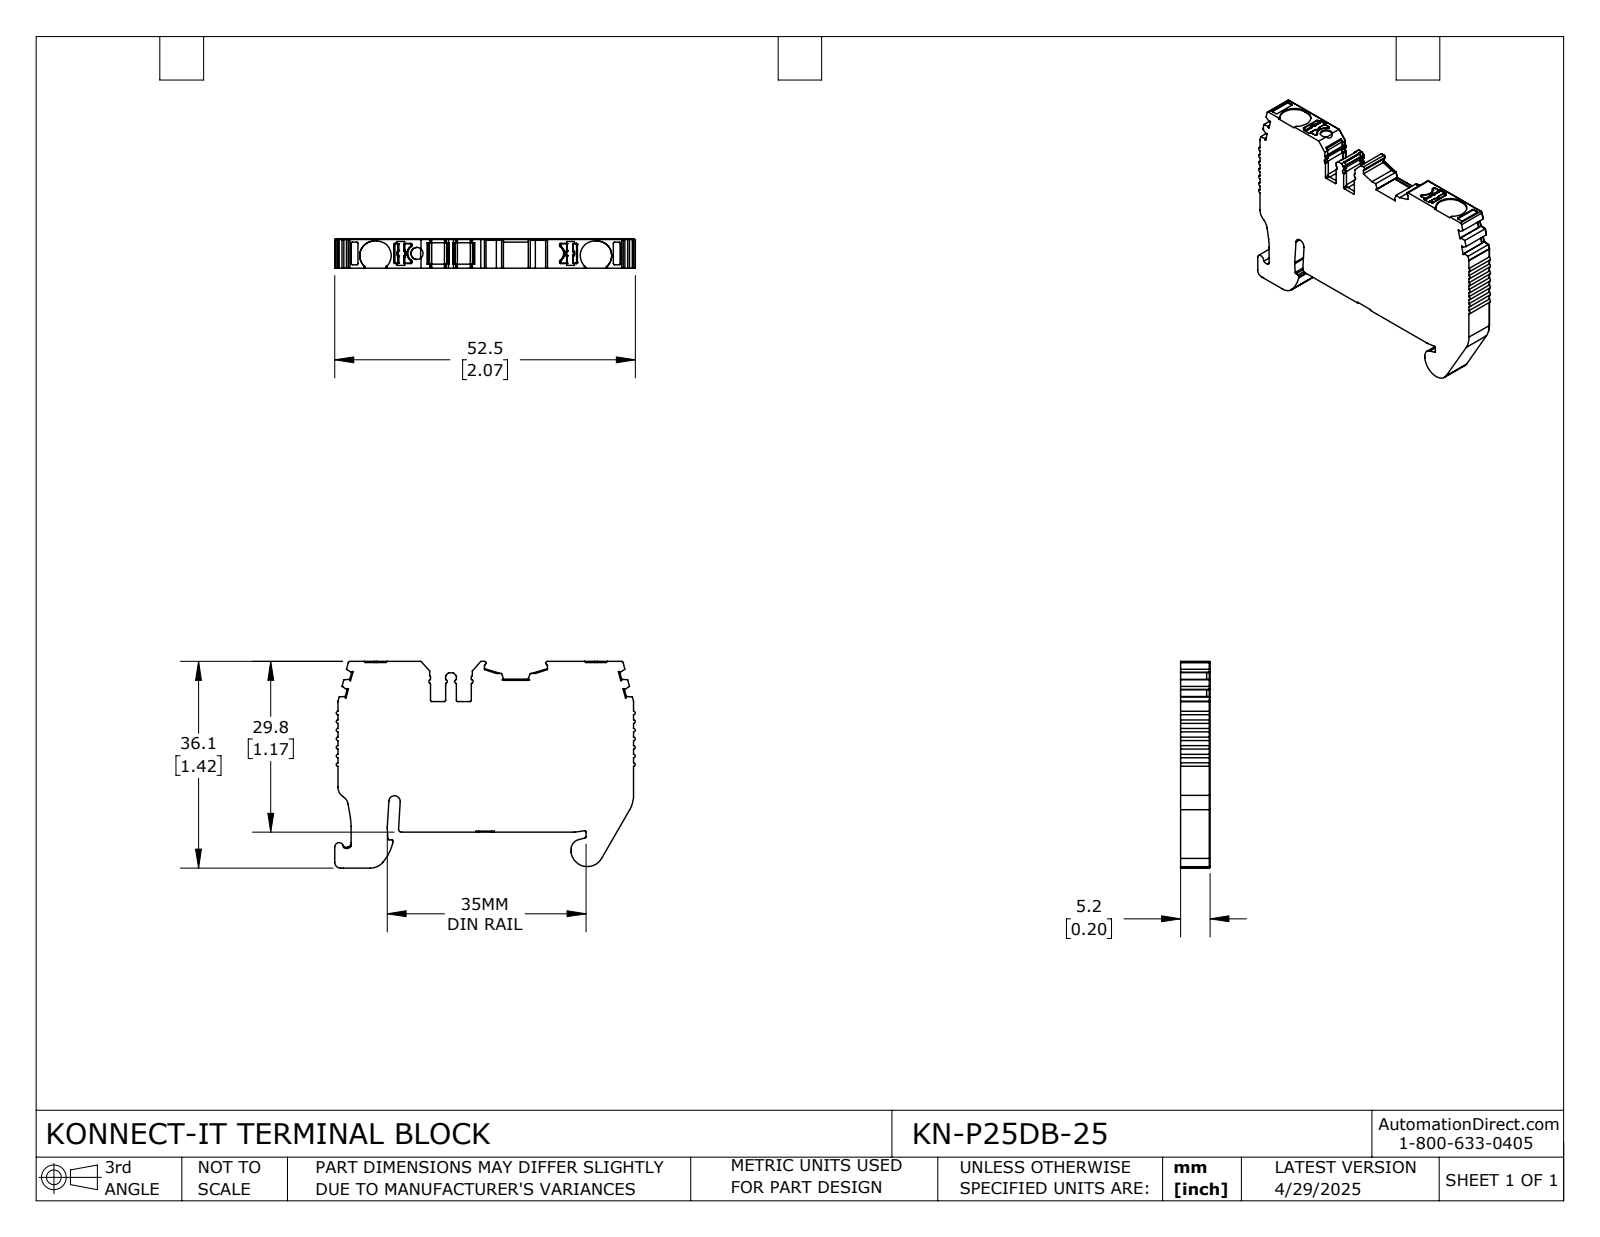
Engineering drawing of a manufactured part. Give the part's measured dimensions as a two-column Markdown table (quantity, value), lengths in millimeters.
| quantity | value |
| --- | --- |
| part name | KN-P25DB-25 |
| STEP written by | SolidWorks 2024 (CONFIG_CONTROL_DESIGN) |
| units | millimeters |
| bodies | 1 solid, 582 faces (308 planar, 239 cylindrical, 35 other) |
| overall size | 52.48 × 36.07 × 5.15 |
| volume | 7 676 mm³ |
| surface area | 4 278 mm² |
| round holes (diameter × count) | 2.1 × 1 |
| partial cylindrical surfaces (radius × count) | 0.2 × 54, 0.3 × 39, 0.5 × 18, 0.1 × 17, 0.4 × 9, 0.15 × 8, 2.55 × 4, 1 × 3 |
| main face-to-face distances | 5.15, 29.61, 29.81, 51.63, 4.5, 5, 6.26, 35.87, 2, 36.07 |
